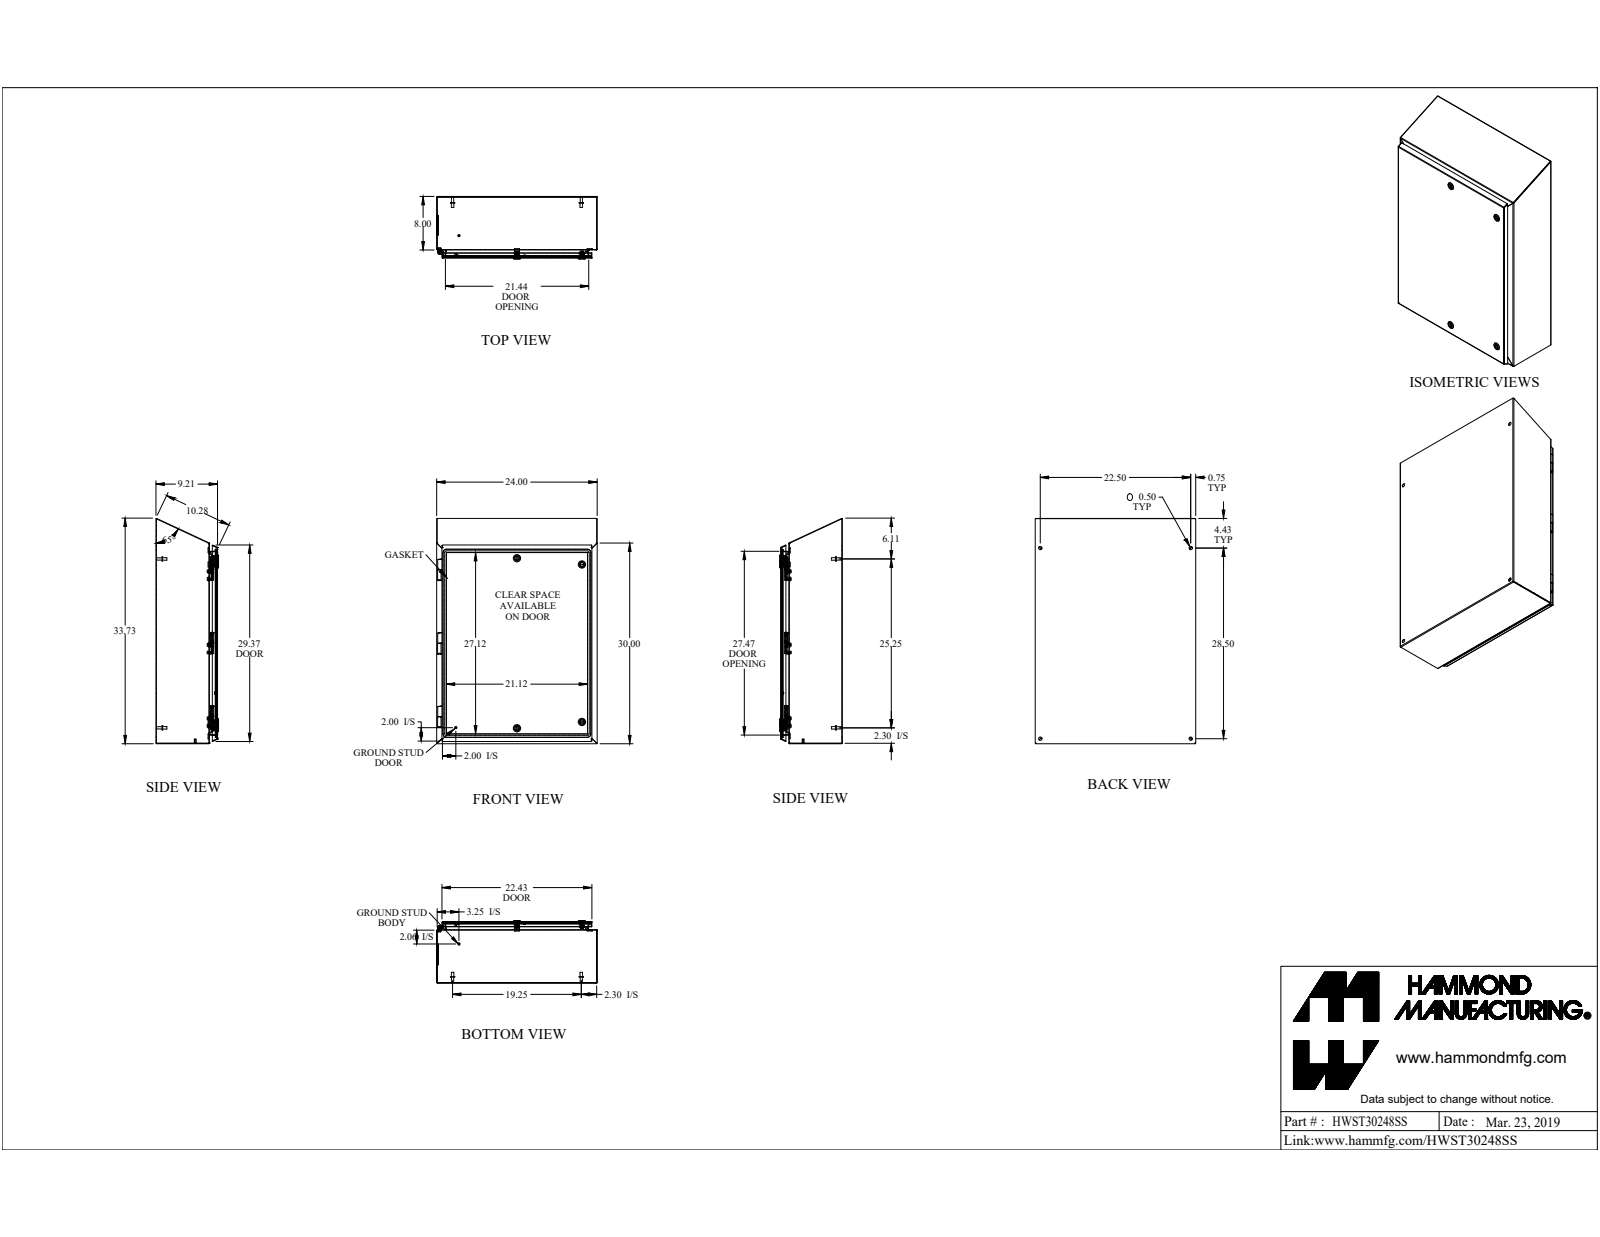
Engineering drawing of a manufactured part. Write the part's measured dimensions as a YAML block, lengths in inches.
part_name: "HWST30248S16"
step_written_by: "SolidWorks 2019 (AUTOMOTIVE_DESIGN)"
units: inches
bodies: {solids: 62, faces: 1442, planar: 901, cylindrical: 401, other: 140}
overall_size: [33.684, 24, 9.37]
volume: 214.9
surface_area: 5816
round_holes:
  - {diameter: 0.5, count: 8}
  - {diameter: 0.194, count: 6}
  - {diameter: 0.194, count: 6}
  - {diameter: 0.24, count: 6}
  - {diameter: 0.275, count: 6}
  - {diameter: 0.197, count: 4}
  - {diameter: 0.387, count: 4}
  - {diameter: 0.63, count: 4}
  - {diameter: 0.768, count: 4}
  - {diameter: 0.13, count: 2}
  - {diameter: 0.24, count: 1}
  - {diameter: 3.5, count: 1}
round_bosses_or_shafts:
  - {diameter: 0.226, count: 12}
  - {diameter: 0.625, count: 10}
  - {diameter: 0.236, count: 5}
  - {diameter: 1.1, count: 4}
  - {diameter: 0.65, count: 4}
  - {diameter: 0.525, count: 4}
  - {diameter: 0.375, count: 4}
  - {diameter: 0.332, count: 4}
partial_cylinders:
  - {radius: 0.039, count: 24}
  - {radius: 0.25, count: 24}
  - {radius: 0.125, count: 20}
  - {radius: 0.012, count: 16}
  - {radius: 0.108, count: 16}
  - {radius: 0.03, count: 14}
  - {radius: 0.036, count: 12}
  - {radius: 0.108, count: 9}
face_to_face_distances: [0.072, 9.066, 9.138, 0.072, 9.138, 9.21, 23.928, 23.856, 24, 7.928]
hole_center_spacings: [1.142, 10.99, 10.989, 21.979, 9.848, 12.131, 9.76, 9.847]
